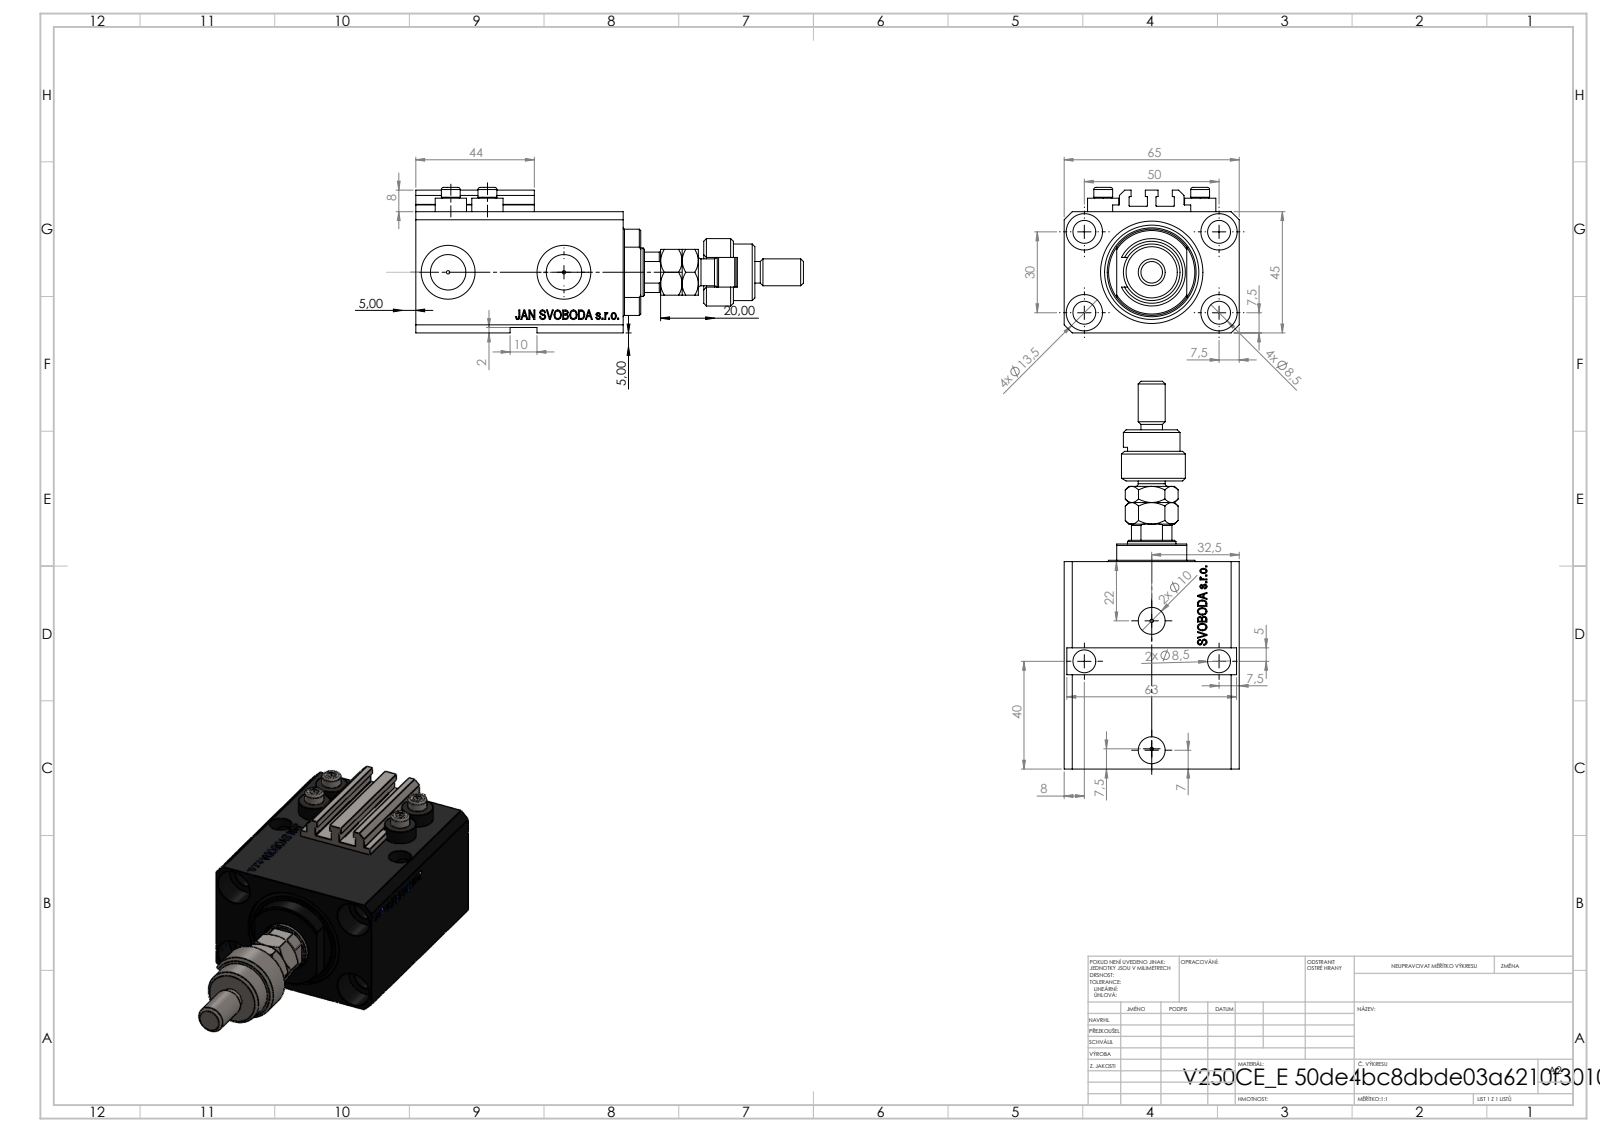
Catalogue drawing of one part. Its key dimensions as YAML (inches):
part_name: "FEMALE_PART_FOR_DFA; V250CE_VC_E; V250CE_C_VCP; MFA (+2 more)"
step_written_by: "SolidWorks 2019 (CONFIG_CONTROL_DESIGN)"
units: inches
bodies: {solids: 10, faces: 1152, planar: 539, cylindrical: 139, other: 474}
overall_size: [5.669, 2.559, 2.126]
volume: 12.91
surface_area: 100.2
round_holes:
  - {diameter: 0.335, count: 7}
  - {diameter: 0.049, count: 4}
  - {diameter: 0.157, count: 4}
  - {diameter: 0.531, count: 4}
  - {diameter: 0.394, count: 2}
  - {diameter: 0.518, count: 2}
  - {diameter: 0.787, count: 2}
  - {diameter: 0.709, count: 1}
  - {diameter: 1.496, count: 1}
round_bosses_or_shafts:
  - {diameter: 0.457, count: 4}
  - {diameter: 0.276, count: 4}
  - {diameter: 0.984, count: 1}
  - {diameter: 0.827, count: 1}
  - {diameter: 0.63, count: 1}
  - {diameter: 0.394, count: 1}
  - {diameter: 0.315, count: 1}
partial_cylinders:
  - {radius: 0.008, count: 10}
  - {radius: 0.217, count: 1}
  - {radius: 0.335, count: 1}
  - {radius: 0.344, count: 1}
  - {radius: 0.63, count: 1}
face_to_face_distances: [1.772, 0.551, 2.559, 2.48, 3.031, 0.079, 0.118, 0.197, 0.272, 2.209]
hole_center_spacings: [1.148, 1.969, 0.535, 0.595, 0.741, 0.747, 1.032, 1.048]
